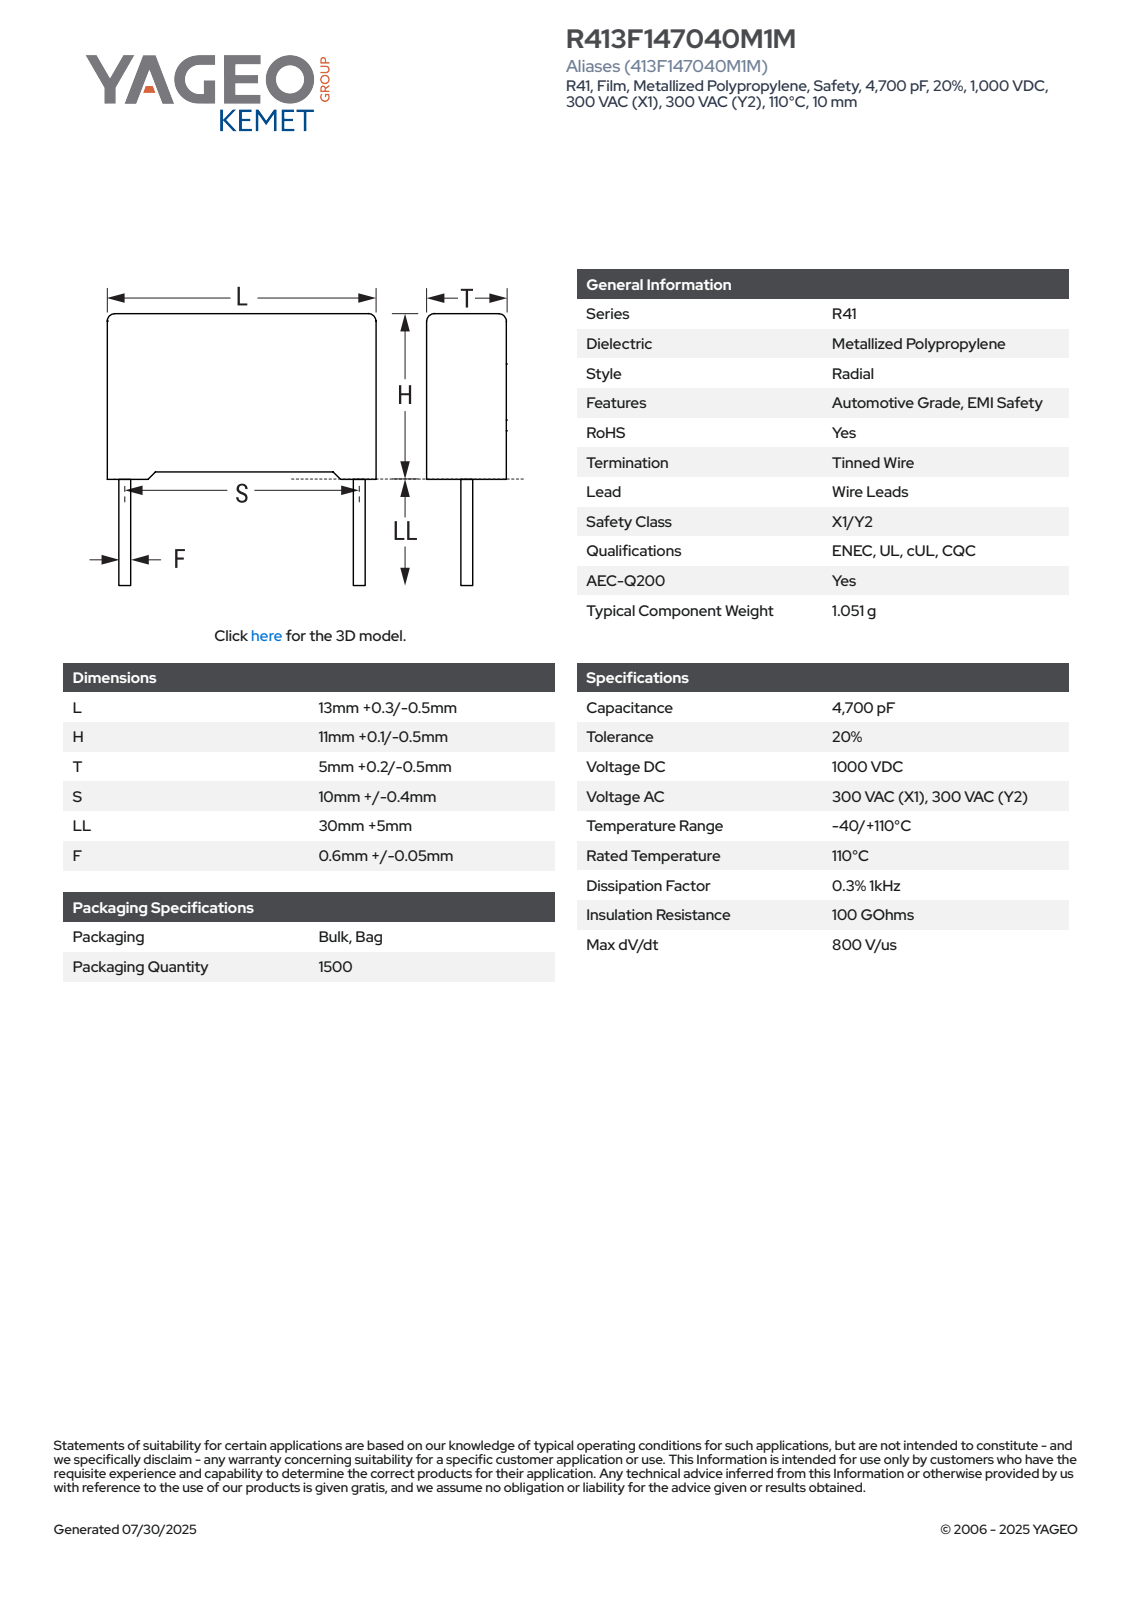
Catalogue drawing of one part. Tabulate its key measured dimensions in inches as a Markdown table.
| quantity | value |
| --- | --- |
| part name | CFR_RB2_13X11X5_L13.3H11.1T5.2S10LL35F0.65 |
| STEP written by | SolidWorks 2021 (AUTOMOTIVE_DESIGN) |
| units | inches |
| bodies | 4 solids, 85 faces (77 planar, 8 cylindrical, 0 other) |
| overall size | 1.815 × 0.524 × 0.205 |
| volume | 0.046 in³ |
| surface area | 1.11 in² |
| round bosses / shafts (diameter × count) | 0.026 × 2 |
| partial cylindrical surfaces (radius × count) | 0.02 × 4 |
| main face-to-face distances | 0.205, 0.524, 0.407, 0.017, 0.187, 0.03, 0.437, 0.17, 0.506, 0.015 |
